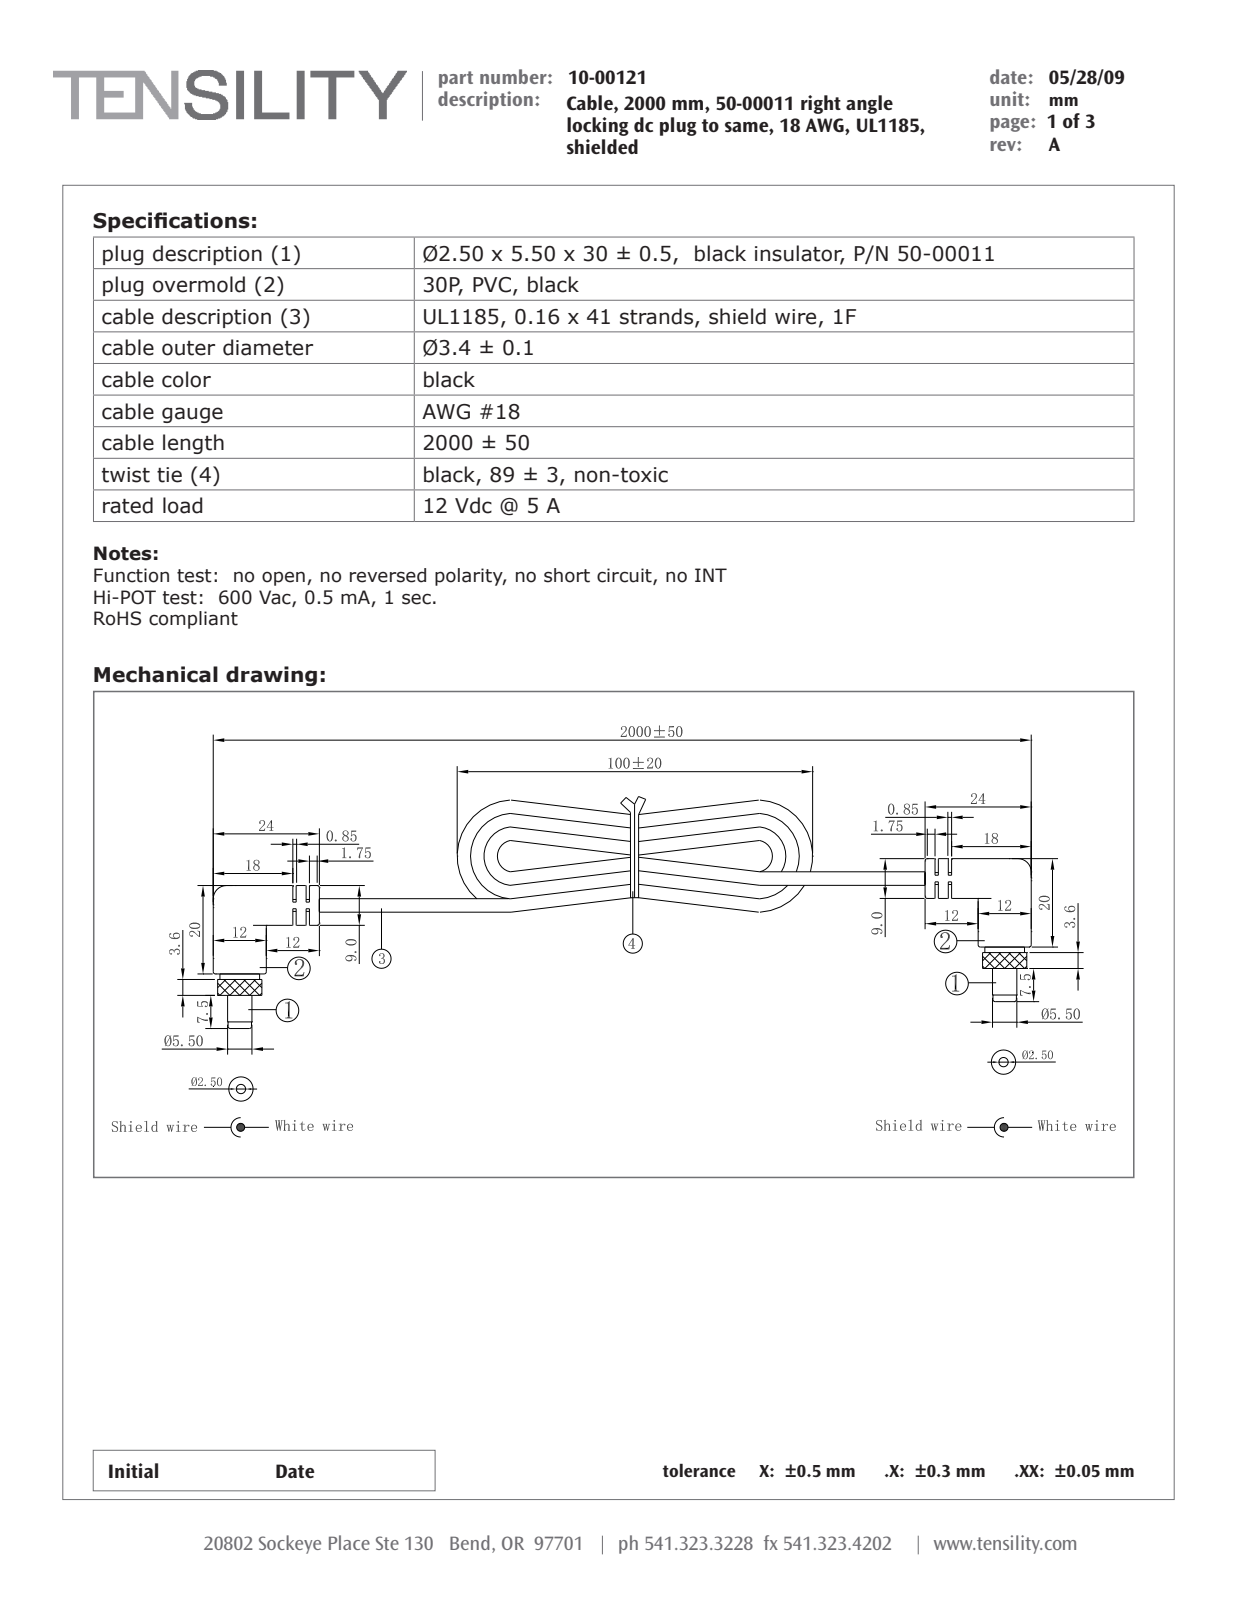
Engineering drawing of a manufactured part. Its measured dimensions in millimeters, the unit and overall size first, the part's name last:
Units: millimetres
Overall size (bounding box): 183 × 32.4 × 11
Round holes (diameter × count): ⌀1.6 ×2, ⌀2.16 ×2, ⌀2.5 ×2, ⌀3 ×2, ⌀3.25 ×2, ⌀4.25 ×2, ⌀5.04 ×2, ⌀5.44 ×2, ⌀5.5 ×2, ⌀5.65 ×2, ⌀6.4 ×2, ⌀7.25 ×2
Round bosses / shafts (diameter × count): ⌀11 ×2, ⌀10 ×2, ⌀7 ×2, ⌀6.2 ×2, ⌀6 ×2, ⌀5.48 ×2, ⌀5.3 ×2, ⌀8.5 ×1
Partial cylindrical surfaces — rounded edges, fillets, slot ends (radius × count): R0.55 ×8
Main face-to-face distances: 3, 1, 2, 16.5, 146, 143, 1.8, 18.3, 11.8, 144
Hole centre spacings: 172
Volume: 6 179 mm³ · Surface area: 18 795 mm²
Bodies: 98 solids, 2902 faces (838 planar, 620 cylindrical, 1444 other)
Part name (STEP PRODUCT): 10-00121; 50-00011 shell; 50-00011; 50-00011 pin (+6 more)
STEP written by: SolidWorks 2015 (CONFIG_CONTROL_DESIGN)
